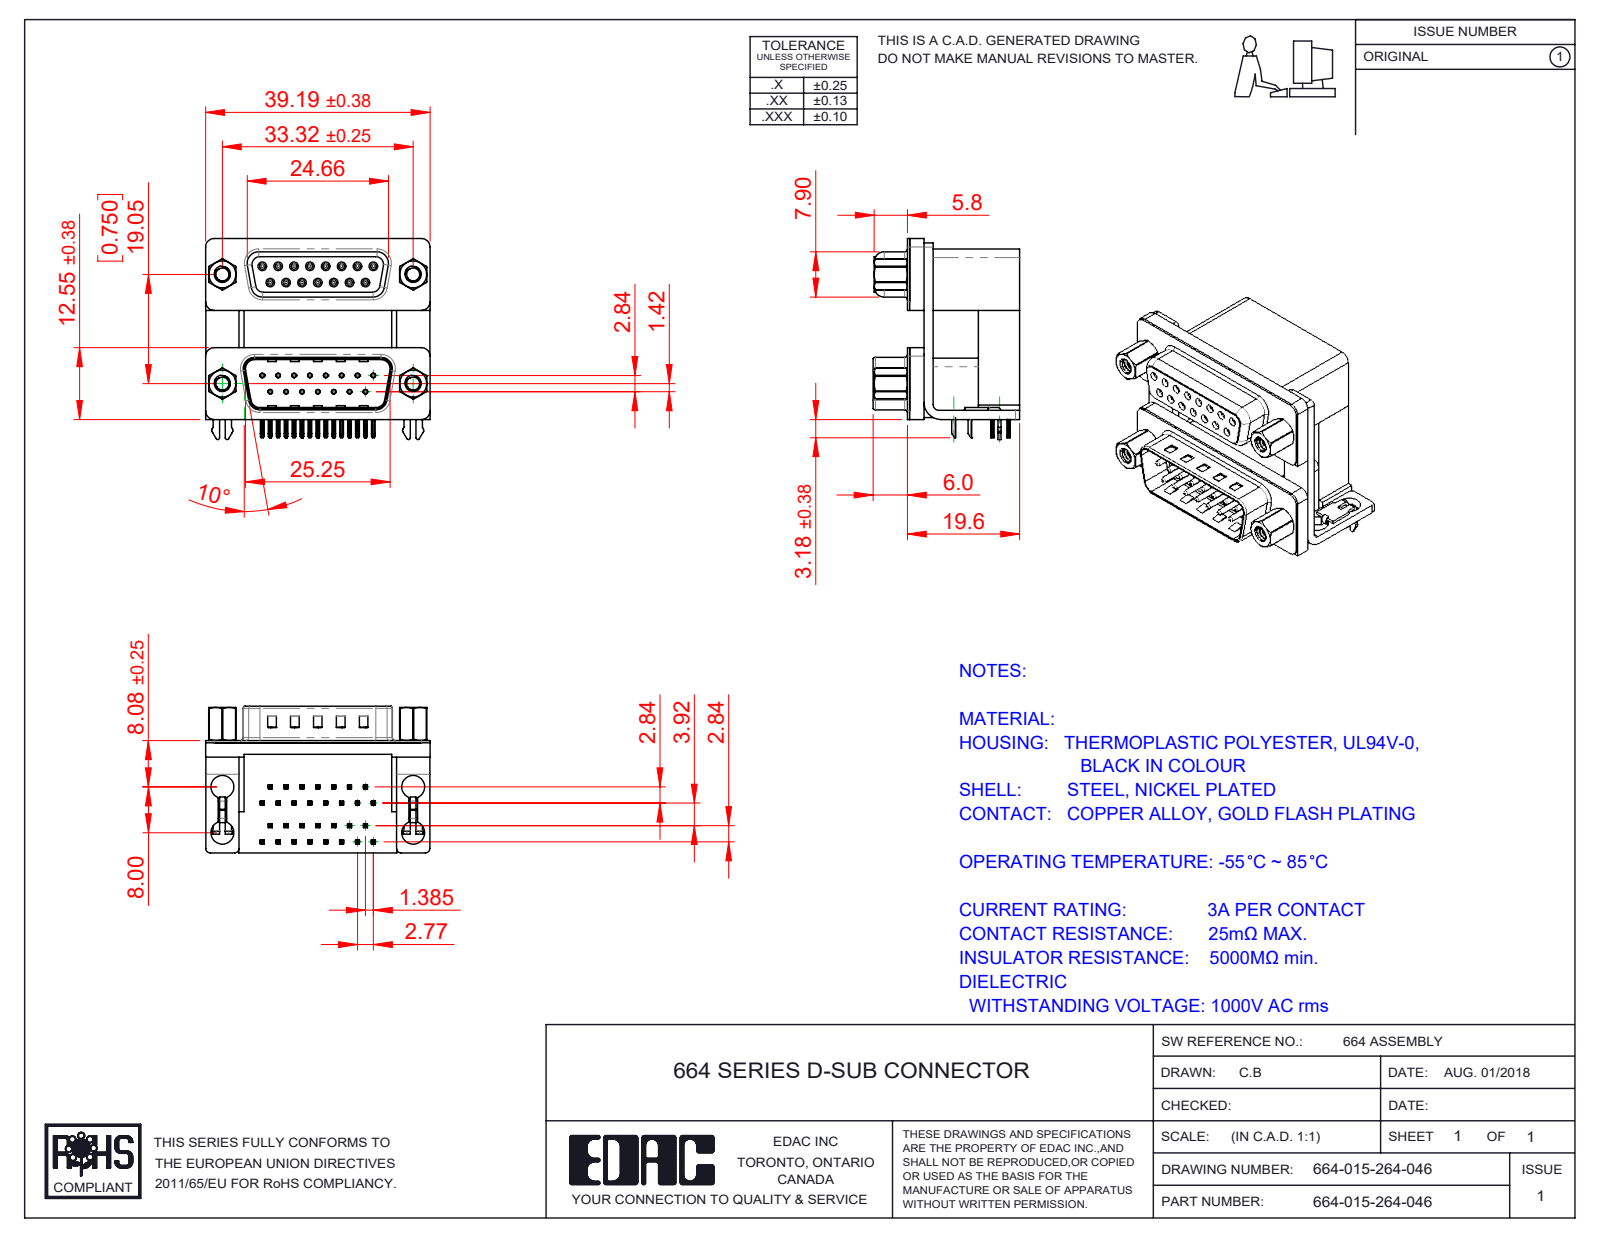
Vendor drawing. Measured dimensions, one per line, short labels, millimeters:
name: 664 Contact Bottom Lower; 664 Housing Upper_15 Contacts M; 664 2 Prong Board Lock_4; 664 Shell Receptacle_15 Contacts (+8 more)
written by: SolidWorks 2020 (CONFIG_CONTROL_DESIGN)
unit: mm
bodies: 47 solids, 4272 faces (2137 planar, 1188 cylindrical, 947 other)
size: 39.19 × 35.1 × 25.6
volume: 15 591 mm³; area: 17 970 mm²
holes: 30× ⌀0.8, 15× ⌀0.35, 15× ⌀0.9, 8× ⌀4, 4× ⌀2.26, 4× ⌀2.29, 4× ⌀3.5, 4× ⌀4.8, 4× ⌀5
bosses: 15× ⌀1.2, 15× ⌀0.75, 4× ⌀4.9, 4× ⌀4.75, 4× ⌀3.9, 4× ⌀2.79
rounds: 121× R0.1, 66× R0.25, 60× R0.15, 30× R0.12, 30× R0.35, 16× R0.5, 16× R1.5, 15× R0.34
face distances: 0.4, 19.2, 16.7, 2.5, 7.2, 12, 9.5, 10.69, 2.19, 19.6
hole spacings: 3.16, 2.77, 19.25, 5.54, 19.84, 8.31, 19.05, 20.78
